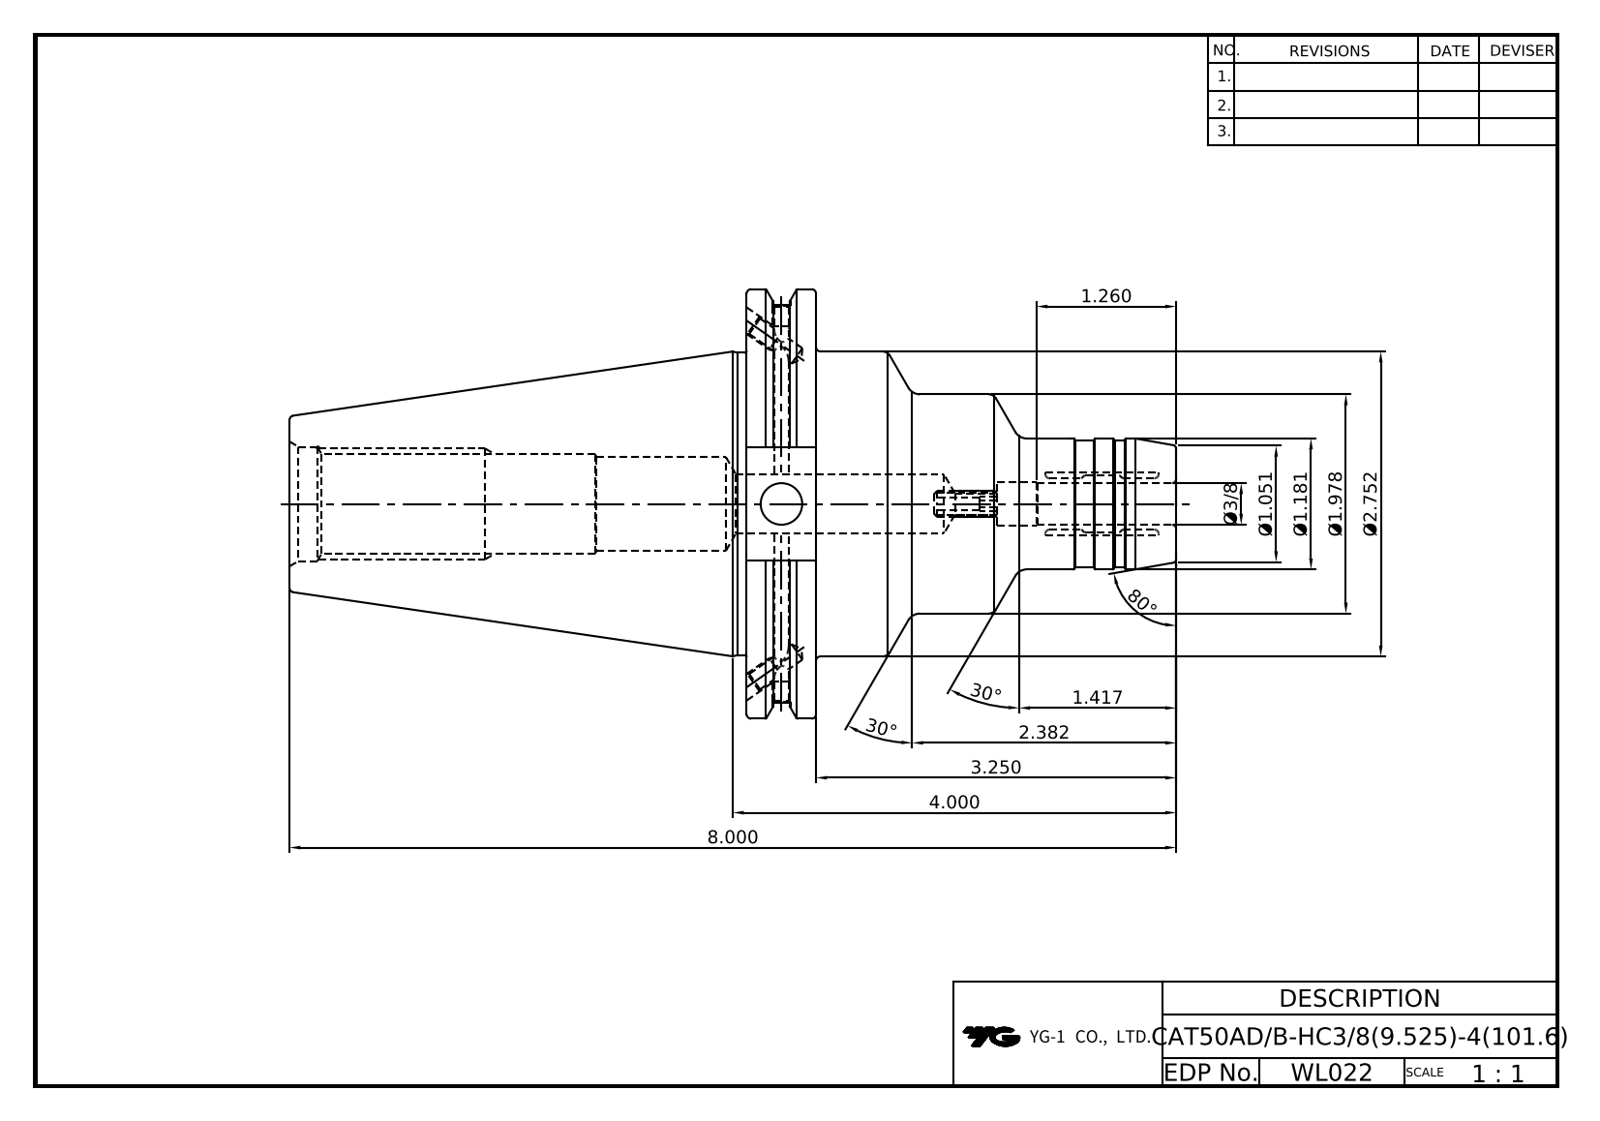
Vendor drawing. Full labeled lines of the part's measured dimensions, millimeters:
Part name (STEP PRODUCT): LO-CAT50ADB-HC9.525-101.6
STEP written by: Autodesk Inventor 2022 (AUTOMOTIVE_DESIGN)
Units: millimetres
Bodies: 1 solid, 112 faces (37 planar, 34 cylindrical, 41 other)
Overall size (bounding box): 203.2 × 98.42 × 94.69
Volume: 464 806 mm³ · Surface area: 57 426 mm²
Round holes (diameter × count): ⌀3.24 ×2, ⌀4.13 ×2, ⌀4.2 ×2, ⌀5 ×2, ⌀4.92 ×1, ⌀9.52 ×1, ⌀9.53 ×1, ⌀10 ×1, ⌀13.5 ×1, ⌀20.5 ×1, ⌀21.97 ×1, ⌀26.2 ×1
Round bosses / shafts (diameter × count): ⌀98.42 ×1, ⌀91.29 ×1, ⌀69.9 ×1, ⌀69.25 ×1, ⌀50.25 ×1, ⌀30 ×1, ⌀29 ×1
Main face-to-face distances: 15.88, 104.77, 120.65, 203.2, 98.43, 82.55, 73.03, 25.9, 110.82, 6.05
